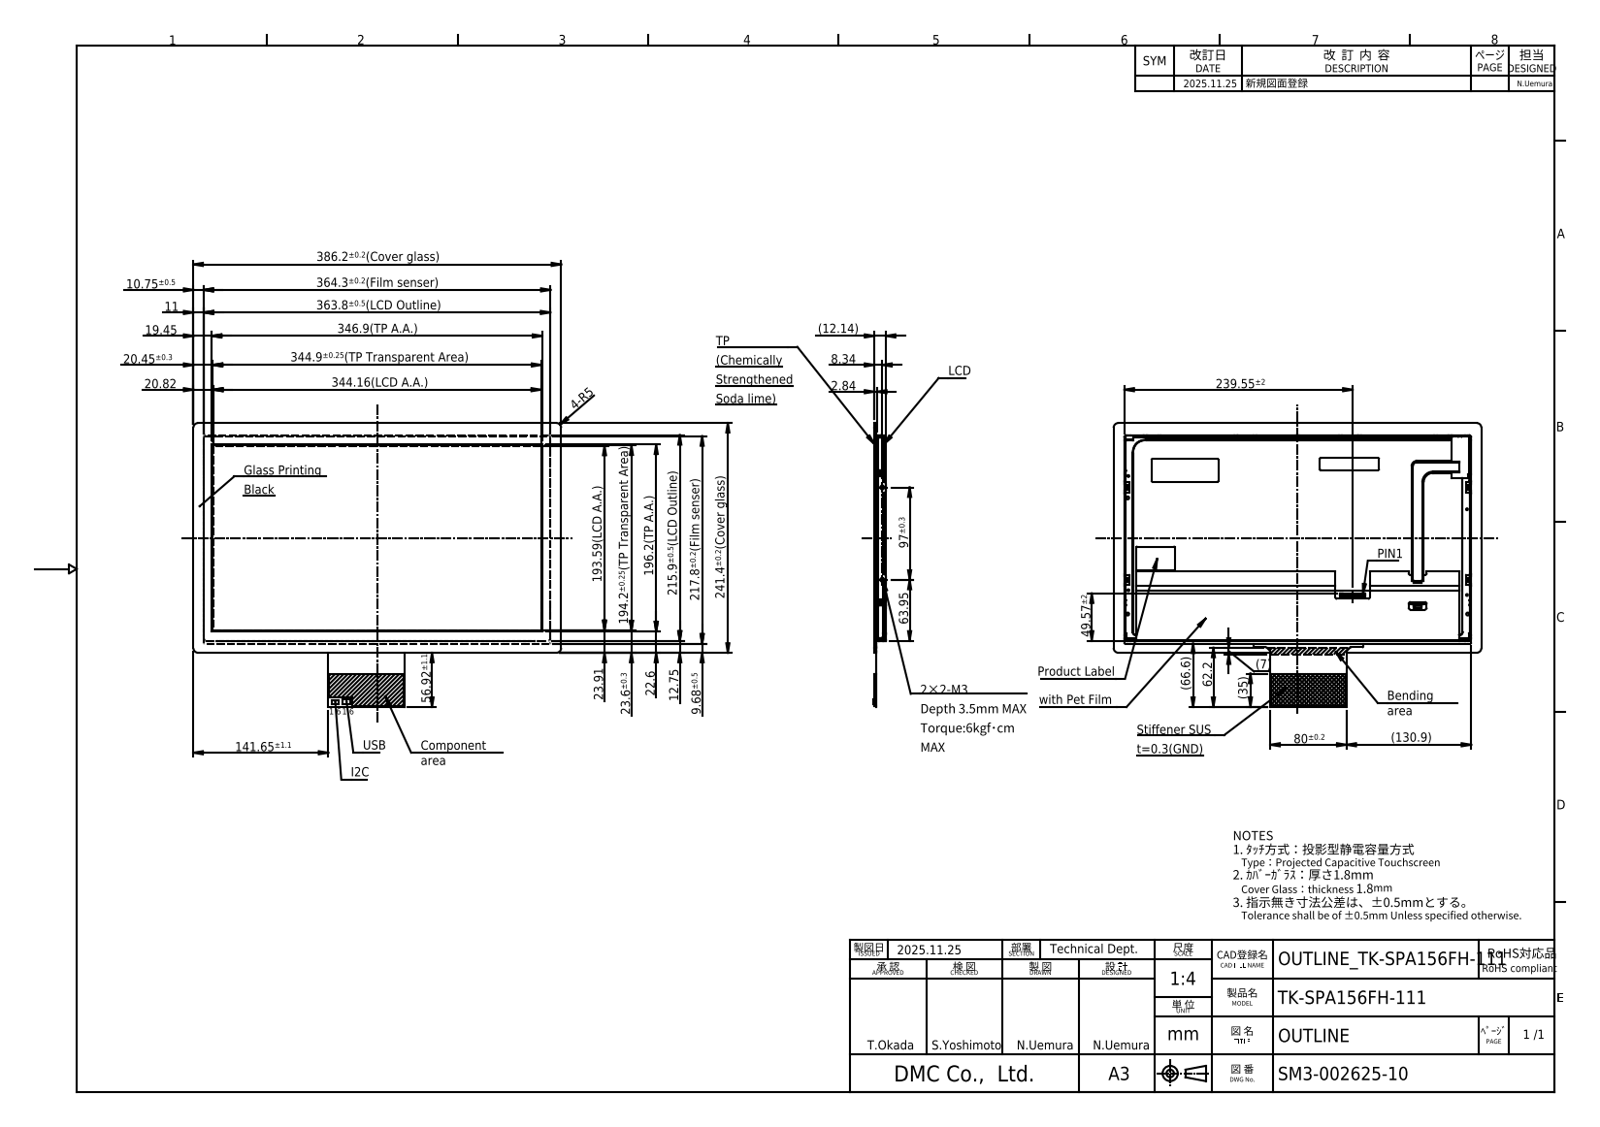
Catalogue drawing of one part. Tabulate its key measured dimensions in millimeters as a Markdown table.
| quantity | value |
| --- | --- |
| part name | TK-SPA156FH-111 |
| STEP written by | Autodesk Inventor 2024 (AUTOMOTIVE_DESIGN) |
| units | millimeters |
| bodies | 1 solid, 3691 faces (2157 planar, 1244 cylindrical, 290 other) |
| overall size | 386.2 × 298.32 × 13.2 |
| volume | 421 839 mm³ |
| surface area | 428 174 mm² |
| round holes (diameter × count) | 0.9 × 4, 3.05 × 4, 3.5 × 3, 3.8 × 3, 0.5 × 2, 2.5 × 2, 3 × 2, 4 × 2 |
| round bosses / shafts (diameter × count) | 2.5 × 4, 6 × 3, 1.97 × 3, 4.6 × 2 |
| partial cylindrical surfaces (radius × count) | 1 × 143, 0.3 × 128, 0.5 × 94, 0.1 × 70, 0.2 × 58, 0.8 × 44, 0.6 × 23, 2 × 21 |
| main face-to-face distances | 3.96, 8.99, 5.03, 0.8, 5.83, 9.79, 2.25, 0.9, 1.45, 2.35 |
| hole center spacings | 97, 9.3, 9.7, 20, 20.01, 20.73, 21.75, 23.01 |
